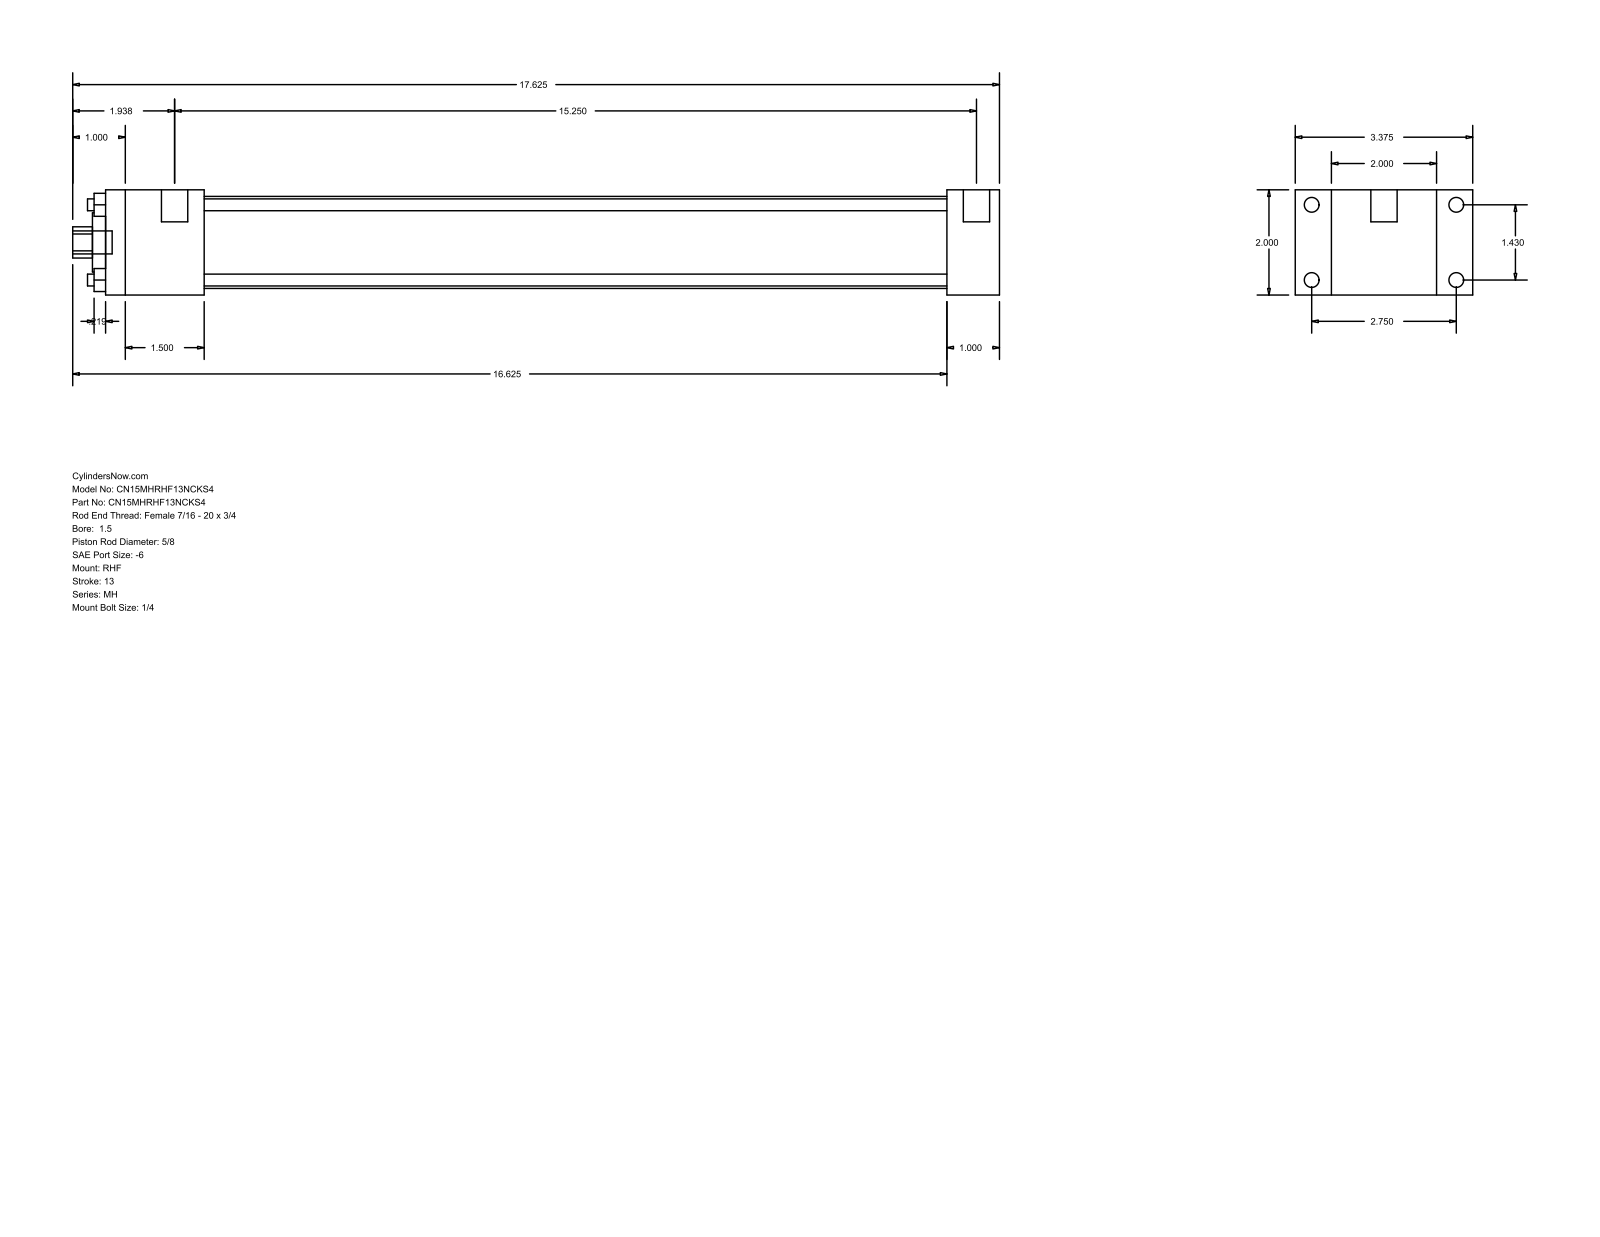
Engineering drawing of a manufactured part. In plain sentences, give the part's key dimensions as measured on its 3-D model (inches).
The part is named "MH_RHF__0150_0.625". Its 3-D file was written by "GSSL Pune (CONFIG_CONTROL_DESIGN)". It is 0 solids with 88 faces: 60 planar, 28 cylindrical and 0 other. Overall it measures 17.625 by 3.375 by 2 inches. Round holes: 4 of diameter 0.225, 1 of diameter 0.625, 1 of diameter 1.125, 1 of diameter 1.75. Round bosses or shafts: 4 of diameter 0.281, 4 of diameter 0.219, 2 of diameter 0.5, 1 of diameter 0.437. Partial cylindrical surfaces (rounded edges, fillets, slot ends): 1 of radius 0.297. The main face-to-face distances are 2, 0.687, 2.687, 1, 16, 17, 3.375, 1.875, 14.125, 15.125. The hole center spacings are 1.011, 1.43, 2.022.
